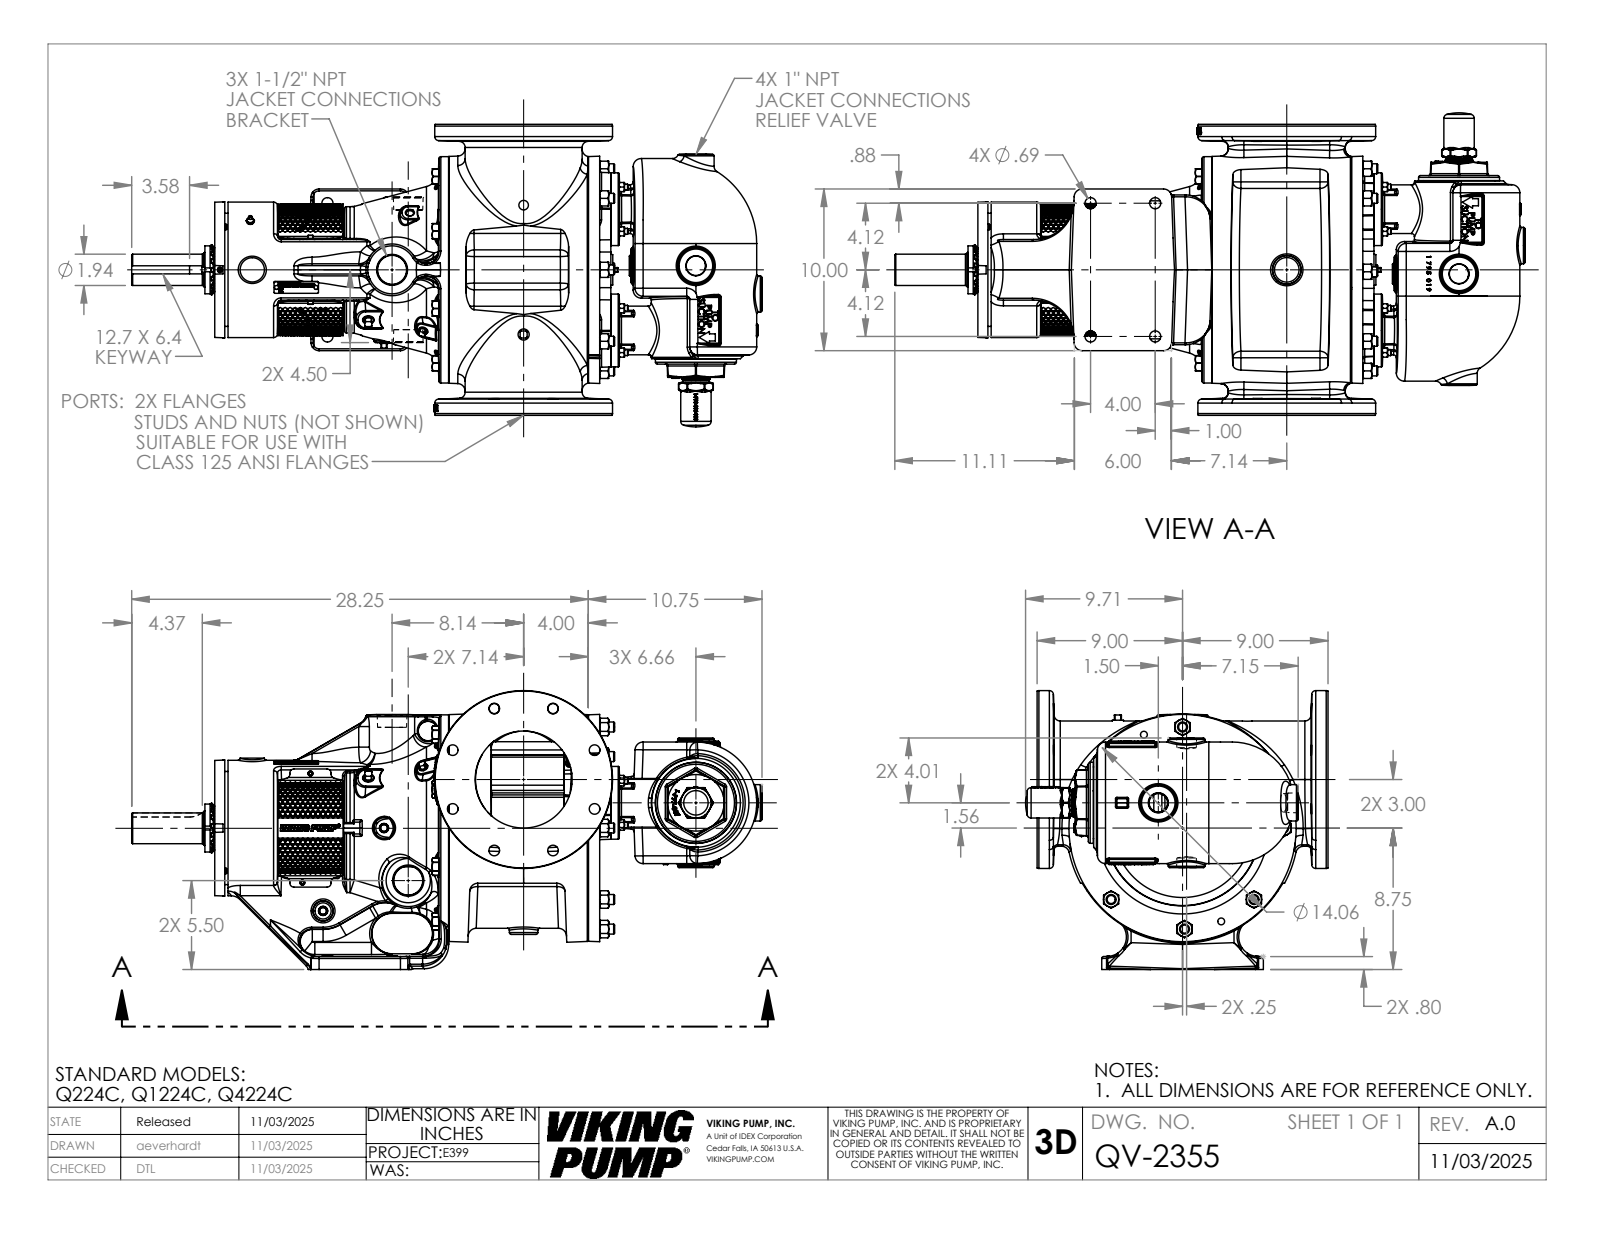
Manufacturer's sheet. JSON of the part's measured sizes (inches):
{"part_name": "QV-2355", "step_written_by": "SolidWorks 2024 (AUTOMOTIVE_DESIGN)", "units": "inches", "bodies": {"solids": 1, "faces": 5204, "planar": 1655, "cylindrical": 777, "other": 2772}, "overall_size": [38.999, 22.94, 17.25], "volume_in3": 3150, "surface_area_in2": 2831, "round_holes": [[0.266, 8], [0.656, 8], [1.157, 8], [0.25, 6], [0.688, 4], [0.159, 2], [0.313, 2], [0.422, 2], [0.453, 1], [1, 1], [2.157, 1], [2.167, 1]], "round_bosses_or_shafts": [[0.75, 8], [0.742, 8], [0.617, 8], [0.369, 8], [0.437, 3], [0.312, 3], [4.5, 2], [0.375, 2]], "partial_cylinders_radius": [[0.12, 60], [0.5, 38], [0.06, 26], [0.75, 22], [0.015, 18], [0.092, 18], [0.07, 16], [0.19, 16]], "face_to_face_distances": [1.5, 18, 16.5, 23.817, 15, 3.82, 19.998, 22.317, 18.498, 6], "hole_center_spacings": [3.75, 2.079, 5.783, 2.713, 3.133, 3.788, 5.423, 5.932]}
